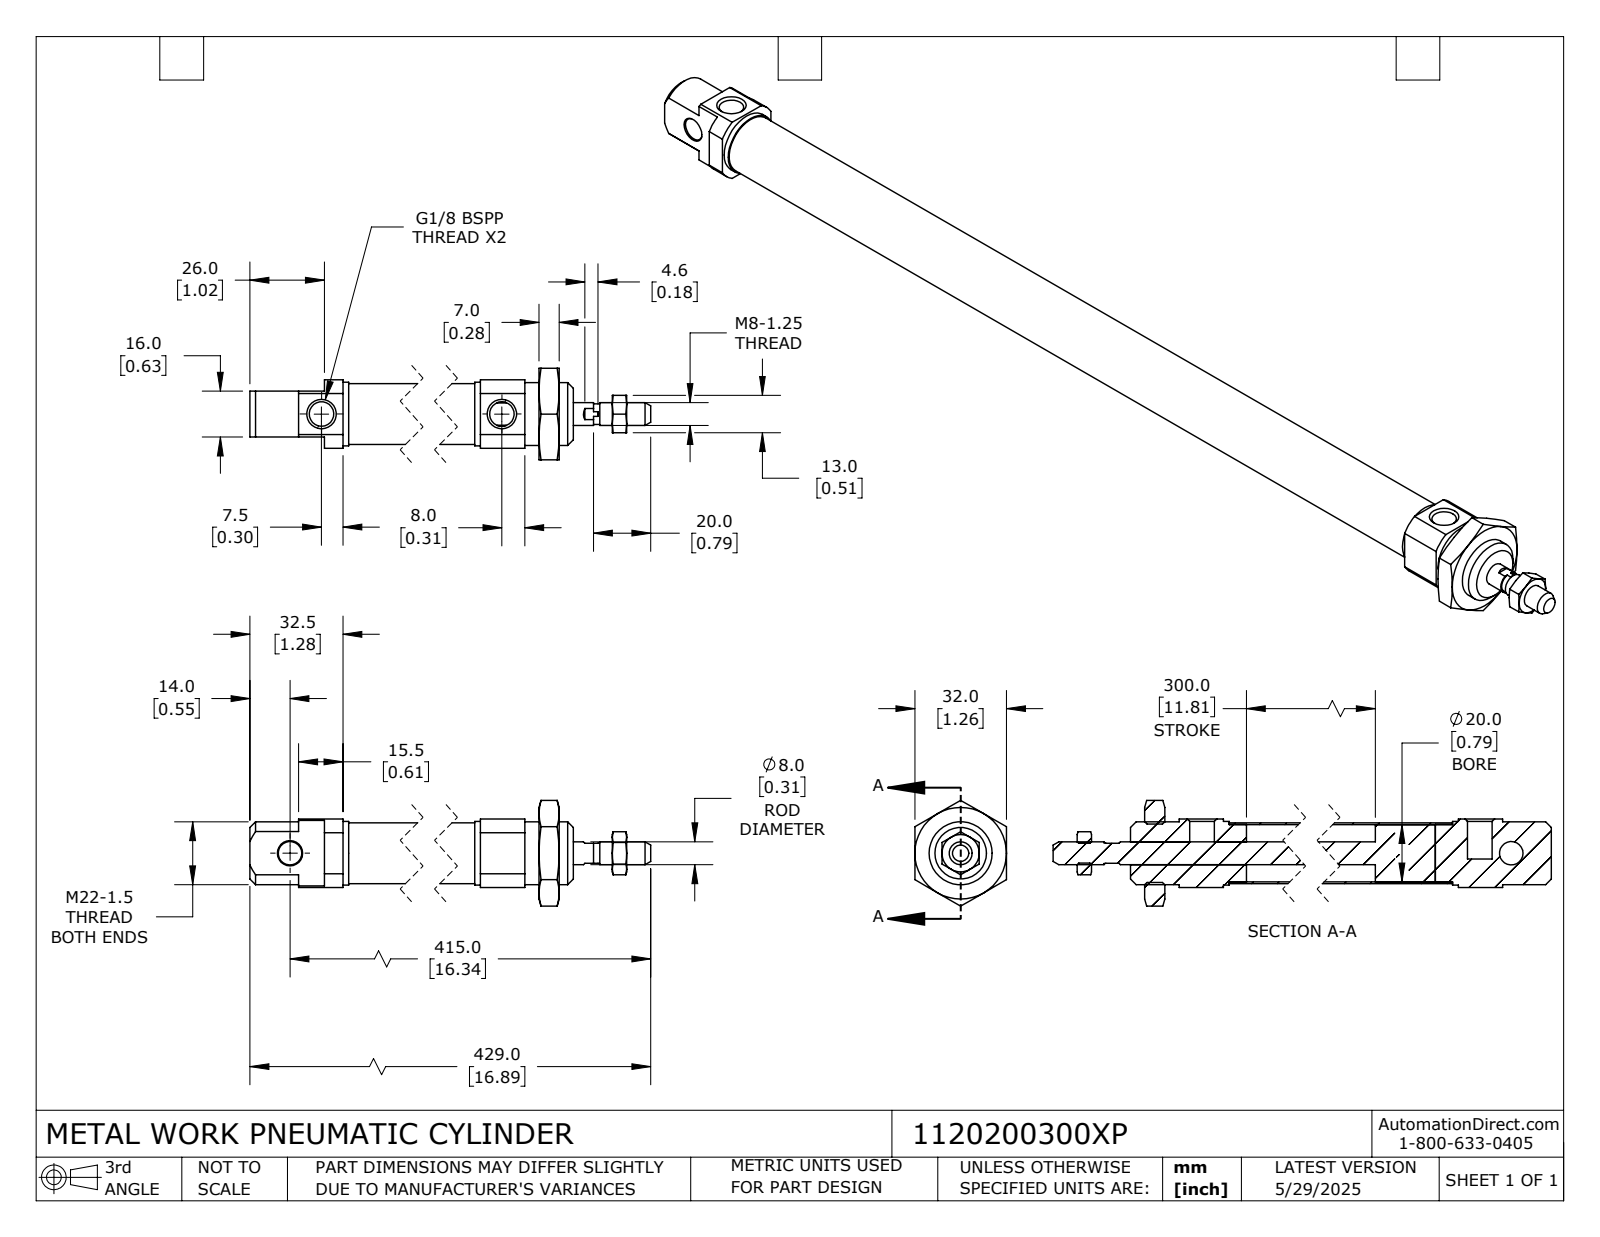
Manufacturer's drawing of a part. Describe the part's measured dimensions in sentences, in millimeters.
The part is named "1120200300XP; 1120200300XP_BODY; 1120200300XP_ROD". Its 3-D file was written by "SolidWorks 2024 (CONFIG_CONTROL_DESIGN)". It is 6 solids with 147 faces: 56 planar, 45 cylindrical and 46 other. Overall it measures 429 by 36.95 by 32 millimeters. Its volume is 71 134 cubic millimeters and its surface area 66 798 square millimeters. Round holes: 2 of diameter 8.57, 1 of diameter 6.92, 1 of diameter 8.2, 1 of diameter 20, 1 of diameter 20.38. Round bosses or shafts: 1 of diameter 22.2, 1 of diameter 22, 1 of diameter 21.27, 1 of diameter 20.15, 1 of diameter 8, 1 of diameter 7.2. Partial cylindrical surfaces (rounded edges, fillets, slot ends): 1 of radius 13.95. The main face-to-face distances are 3.97, 19.97, 23.94, 8, 40.5, 361.5, 7, 5, 356.5, 349.5. The hole center spacings are 352.
